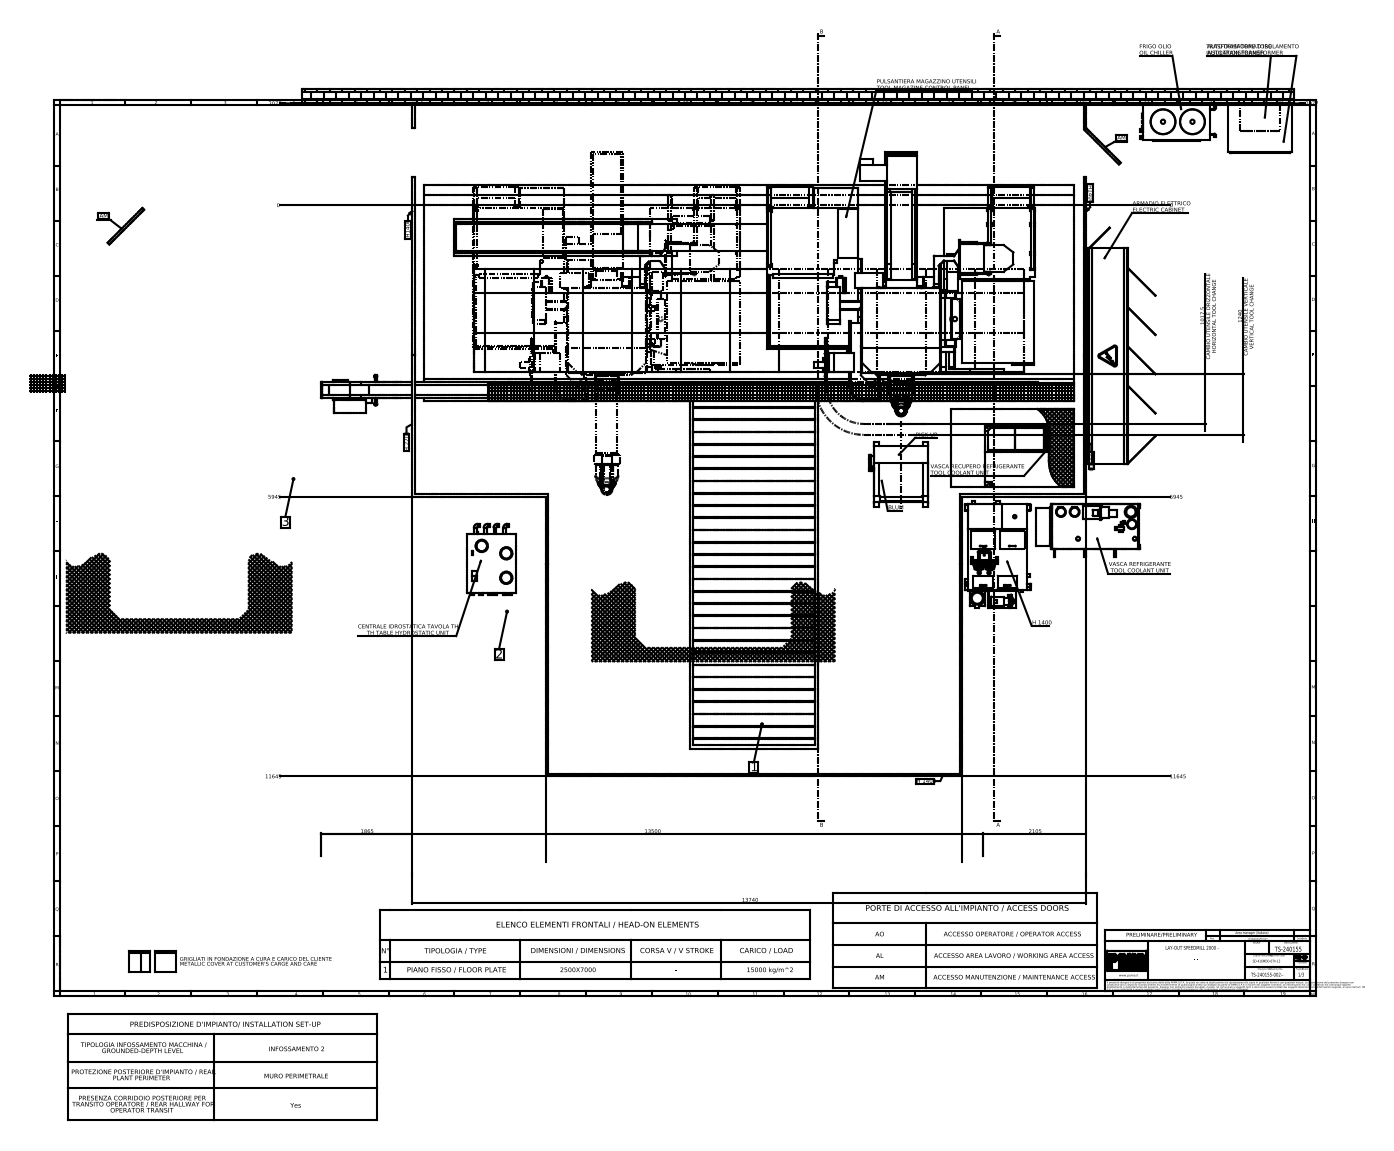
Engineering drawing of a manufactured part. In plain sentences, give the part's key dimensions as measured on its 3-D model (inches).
The part is named "S003172; S000885_L=895; S003511_ISO 50 - RIPOSO; S003502_TM 2R H3950 (+8 more)". Its 3-D file was written by "SolidWorks 2023 (AUTOMOTIVE_DESIGN)". It is 426 solids with 6486 faces: 4587 planar, 1329 cylindrical and 570 other. Overall it measures 952.642 by 668.189 by 370.079 inches. Its volume is 43 670 000 cubic inches and its surface area 3 224 000 square inches. Round holes: 64 of diameter 1.378, 63 of diameter 2.74, 8 of diameter 0.512, 8 of diameter 0.551, 6 of diameter 0.315, 6 of diameter 1.26, 4 of diameter 0.492, 3 of diameter 1.969, 3 of diameter 2.231, 2 of diameter 0.748, 2 of diameter 1.181, 2 of diameter 2.236. Round bosses or shafts: 14 of diameter 0.787, 10 of diameter 0.354, 8 of diameter 2.165, 8 of diameter 1.181, 7 of diameter 2.61, 6 of diameter 2.362, 6 of diameter 1.378, 4 of diameter 7.874. Partial cylindrical surfaces (rounded edges, fillets, slot ends): 141 of radius 0.197, 46 of radius 0.591, 36 of radius 0.236, 27 of radius 0.394, 26 of radius 1.378, 19 of radius 0.787, 16 of radius 0.118, 16 of radius 0.315. The main face-to-face distances are 78.74, 11.811, 1.969, 52.756, 25.984, 668.189, 656.378, 796.85, 5.906, 88.583. The hole center spacings are 9.843, 19.685, 29.528, 39.37, 49.213, 59.055, 68.898, 78.74.
